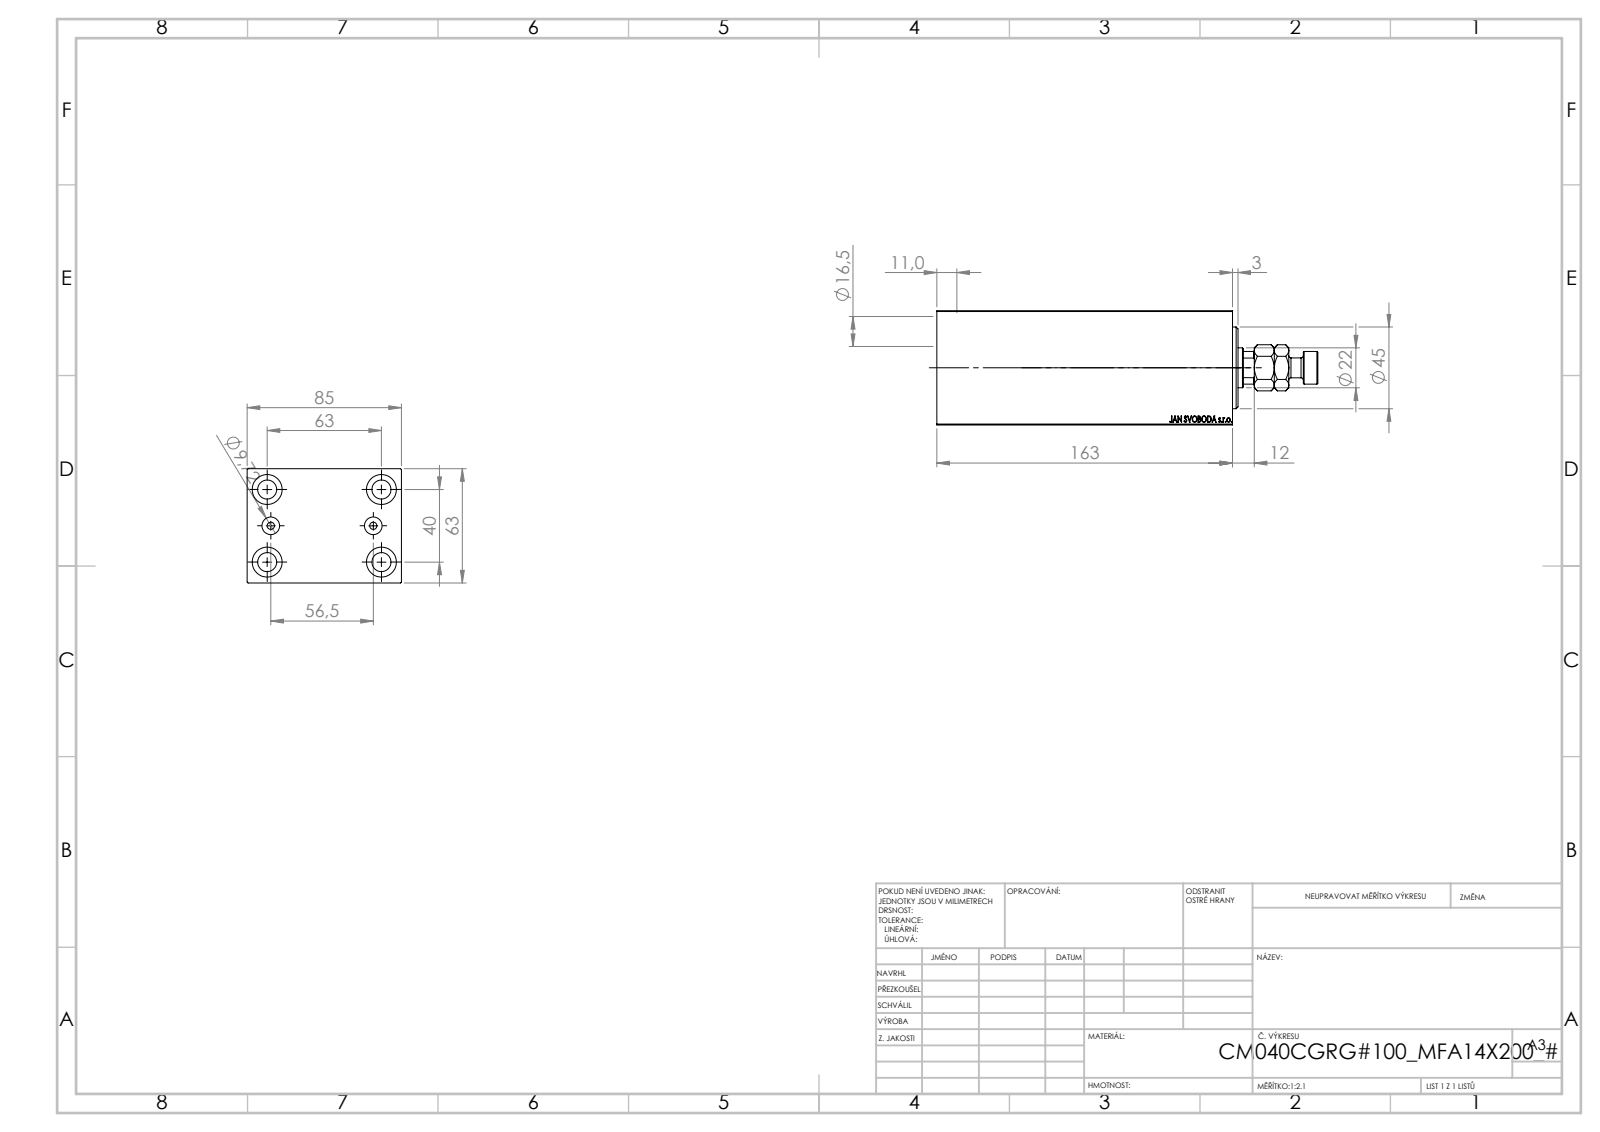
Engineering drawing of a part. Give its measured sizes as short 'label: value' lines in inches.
name: V450CM_VC_B; V450CM_C_Body; V450CM_C_VCP; MFA
written by: SolidWorks 2019 (CONFIG_CONTROL_DESIGN)
unit: in
bodies: 4 solids, 910 faces (424 planar, 60 cylindrical, 426 other)
size: 8.268 × 3.346 × 2.48
volume: 44.42 in³; area: 192.3 in²
holes: 4× ⌀0.413, 4× ⌀0.65, 2× ⌀0.157, 2× ⌀0.383, 1× ⌀0.492, 1× ⌀0.866, 1× ⌀1.004, 1× ⌀1.575, 1× ⌀1.654, 1× ⌀1.772
bosses: 1× ⌀0.709, 1× ⌀0.433
rounds: 1× R0.413
face distances: 2.48, 3.346, 6.417, 5.049, 1.368, 0.394, 6.024, 0.866, 4.656, 0.433
hole spacings: 0.798, 1.469, 2.481, 1.112, 1.575, 2.48, 2.938, 2.224
